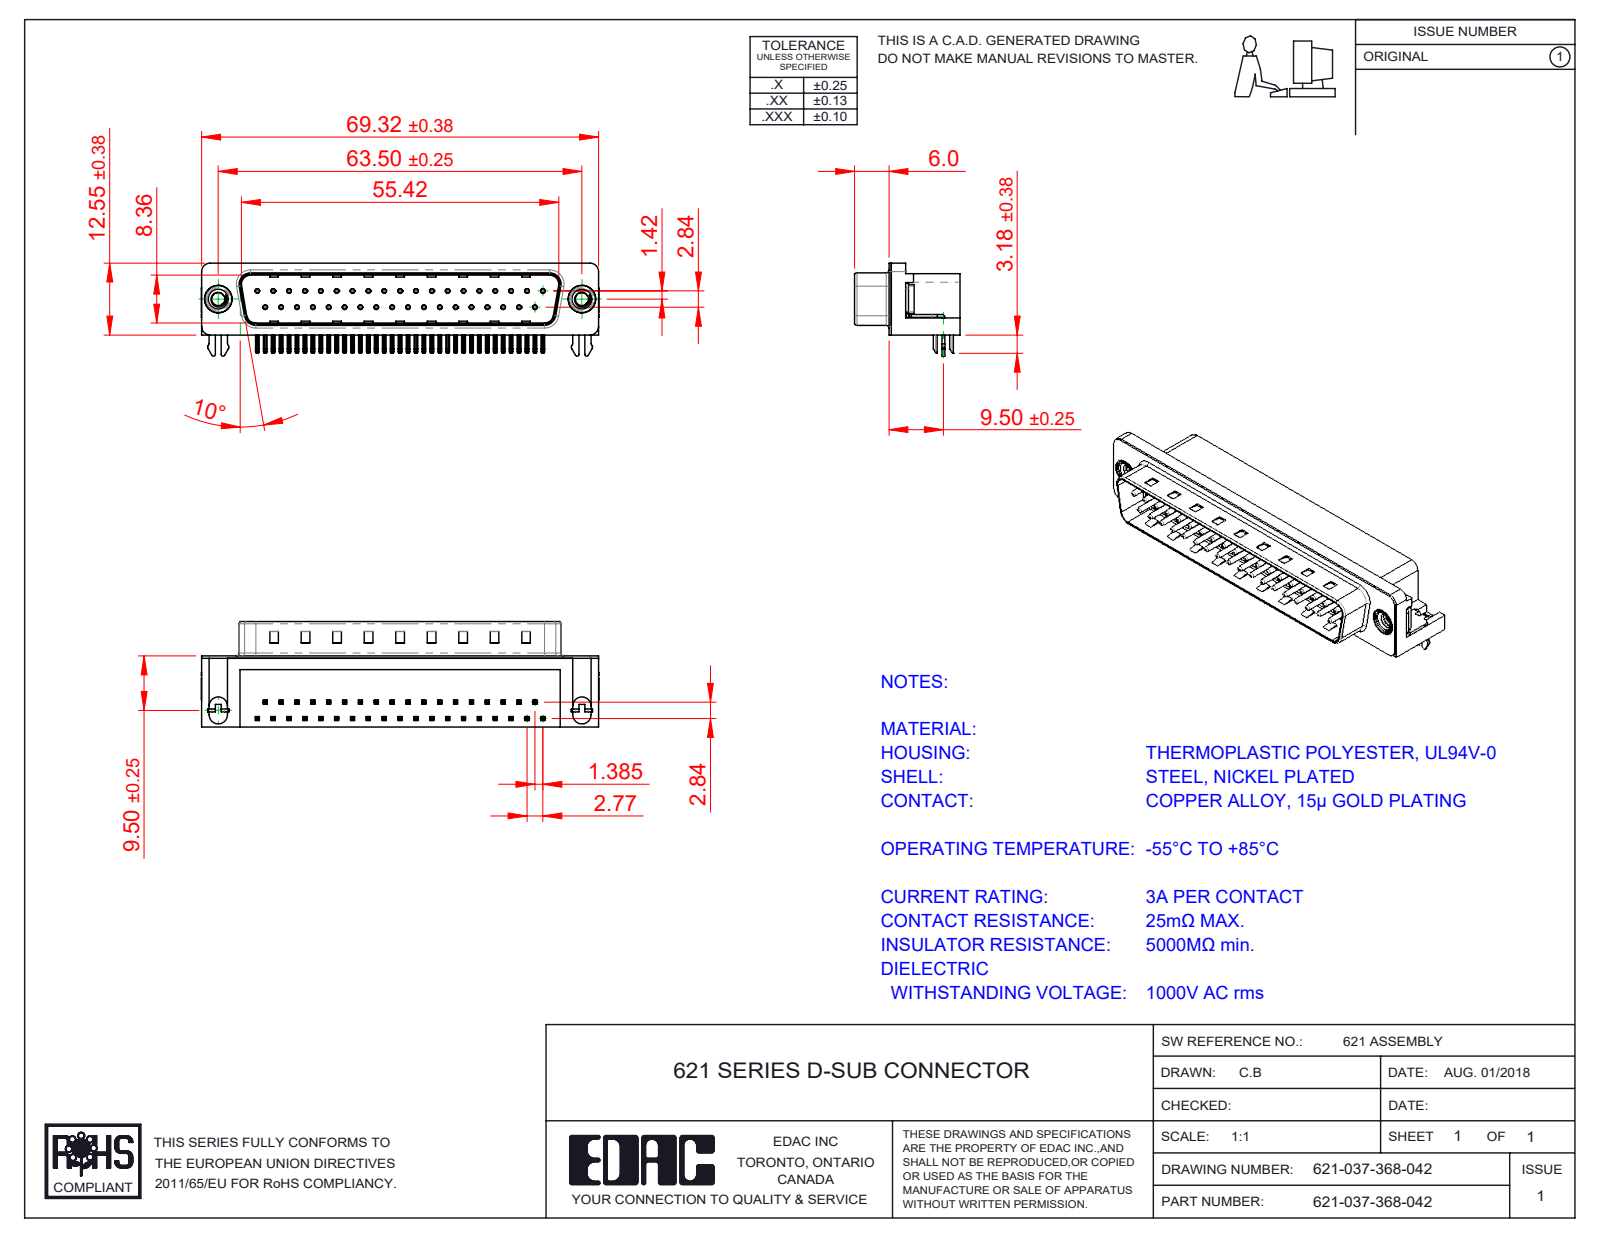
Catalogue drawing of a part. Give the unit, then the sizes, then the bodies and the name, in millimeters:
Units: millimetres
Overall size (bounding box): 69.4 × 18.4 × 16.25
Round holes (diameter × count): ⌀0.35 ×37, ⌀0.8 ×37, ⌀2 ×2, ⌀2.26 ×2, ⌀4 ×2, ⌀4.8 ×2, ⌀5 ×2
Round bosses / shafts (diameter × count): ⌀0.75 ×37, ⌀4.9 ×2, ⌀4.75 ×2, ⌀3.9 ×2, ⌀3 ×2
Partial cylindrical surfaces — rounded edges, fillets, slot ends (radius × count): R0.25 ×160, R0.12 ×74, R1 ×16, R0.5 ×9, R1.6 ×8, R1.5 ×7, R0.9 ×4, R2 ×4
Main face-to-face distances: 0.4, 12, 10.35, 8.76, 2.1, 1.7, 10.46, 10.86, 9, 12.4
Hole centre spacings: 3.16, 2.77, 5.54, 8.31, 11.08, 13.85, 19.39, 22.16
Volume: 8 632 mm³ · Surface area: 10 169 mm²
Bodies: 43 solids, 3319 faces (2055 planar, 921 cylindrical, 343 other)
Part name (STEP PRODUCT): 621 Housing_37 Socket; 621-037-368-042; 621 4-40 Threaded Rivet; 621 Contact Top (+3 more)
STEP written by: SolidWorks 2016 (CONFIG_CONTROL_DESIGN)
